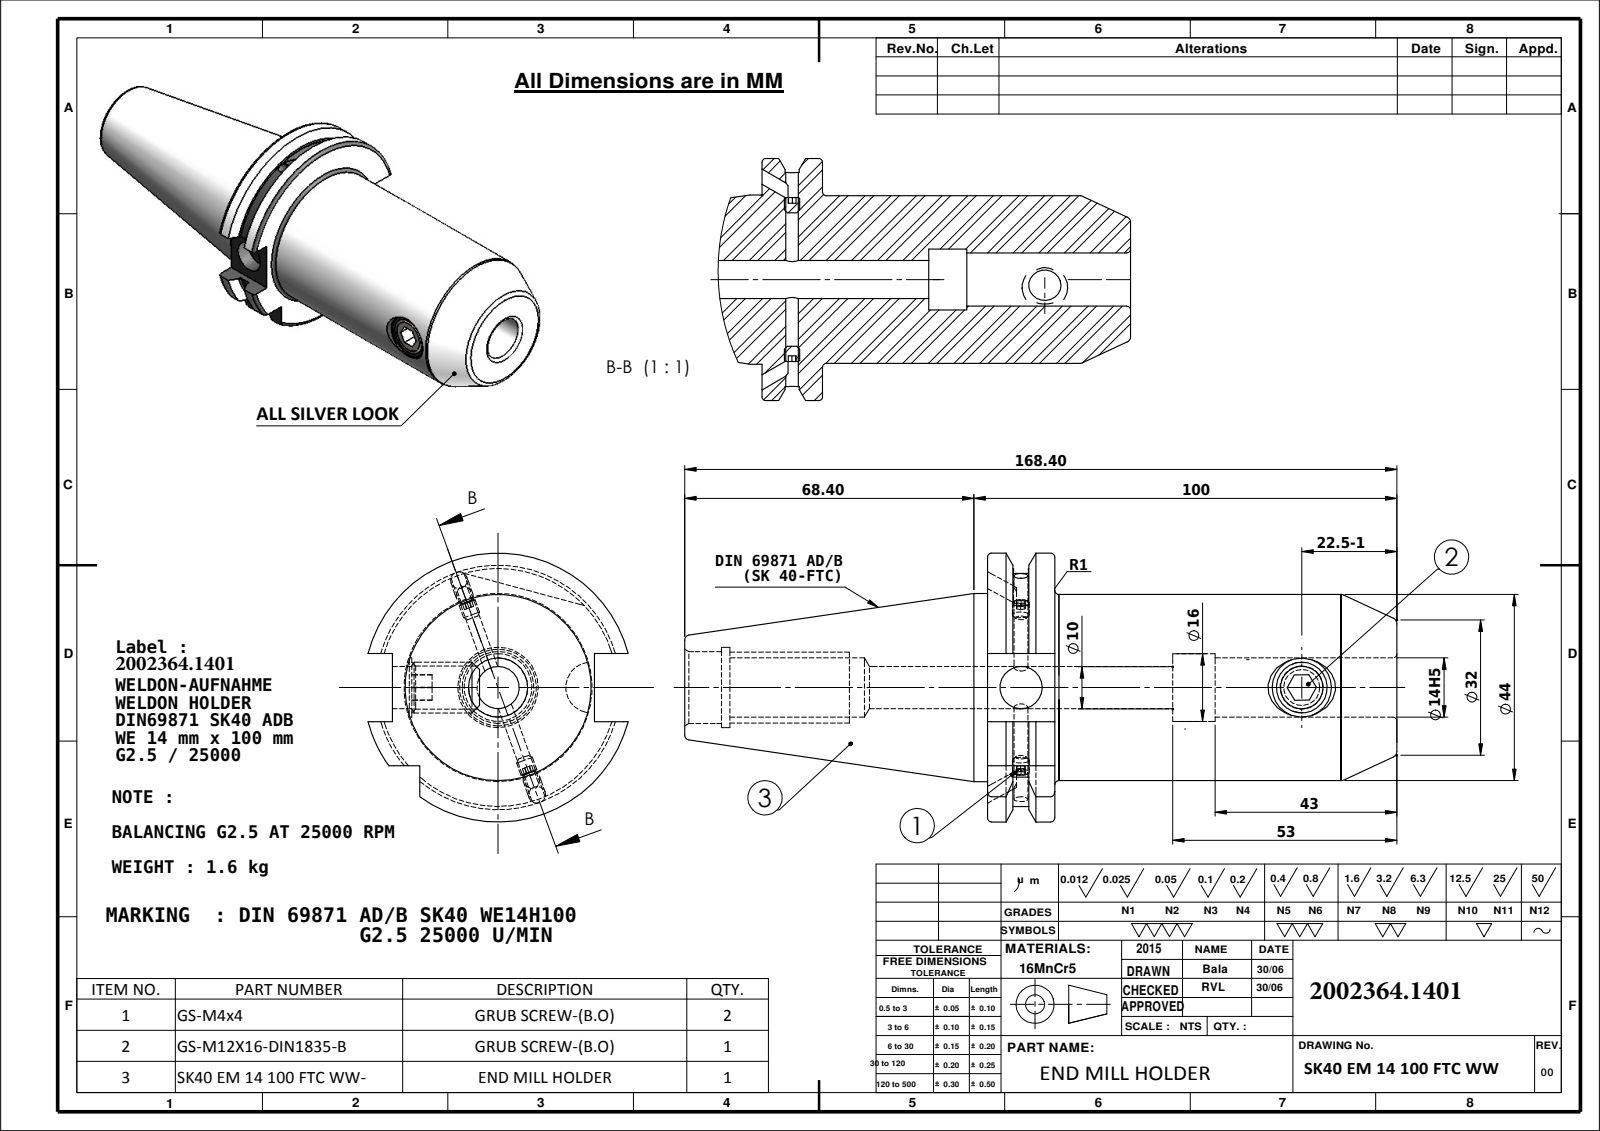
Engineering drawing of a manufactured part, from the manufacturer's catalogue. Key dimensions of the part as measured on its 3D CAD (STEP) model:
Part name (STEP PRODUCT): SK40 EM 14 100 FTC WW; M12X16._ISO 4026 - M12 x 12-N; Copy of M4X4_DIN 913 - M4 x 4-N; 91406-WE7 140100 (+1 more)
STEP written by: SolidWorks 2009 (CONFIG_CONTROL_DESIGN)
Units: millimetres
Bodies: 5 solids, 175 faces (67 planar, 46 cylindrical, 62 other)
Overall size (bounding box): 1074.34 × 954.36 × 382.82
Volume: 208 893 mm³ · Surface area: 36 021 mm²
Round holes (diameter × count): ⌀10 ×2, ⌀14 ×2, ⌀3.3 ×1, ⌀10.2 ×1, ⌀16 ×1, ⌀17 ×1, ⌀19 ×1
Round bosses / shafts (diameter × count): ⌀4 ×3, ⌀44.45 ×1, ⌀44 ×1, ⌀12 ×1
Partial cylindrical surfaces — rounded edges, fillets, slot ends (radius × count): R28.12 ×1, R31.77 ×1
Main face-to-face distances: 15.9, 96.8, 80.9, 16.1, 47.8, 4.6, 43.2, 71.6, 87.5, 168.4
Hole centre spacings: 66.35
